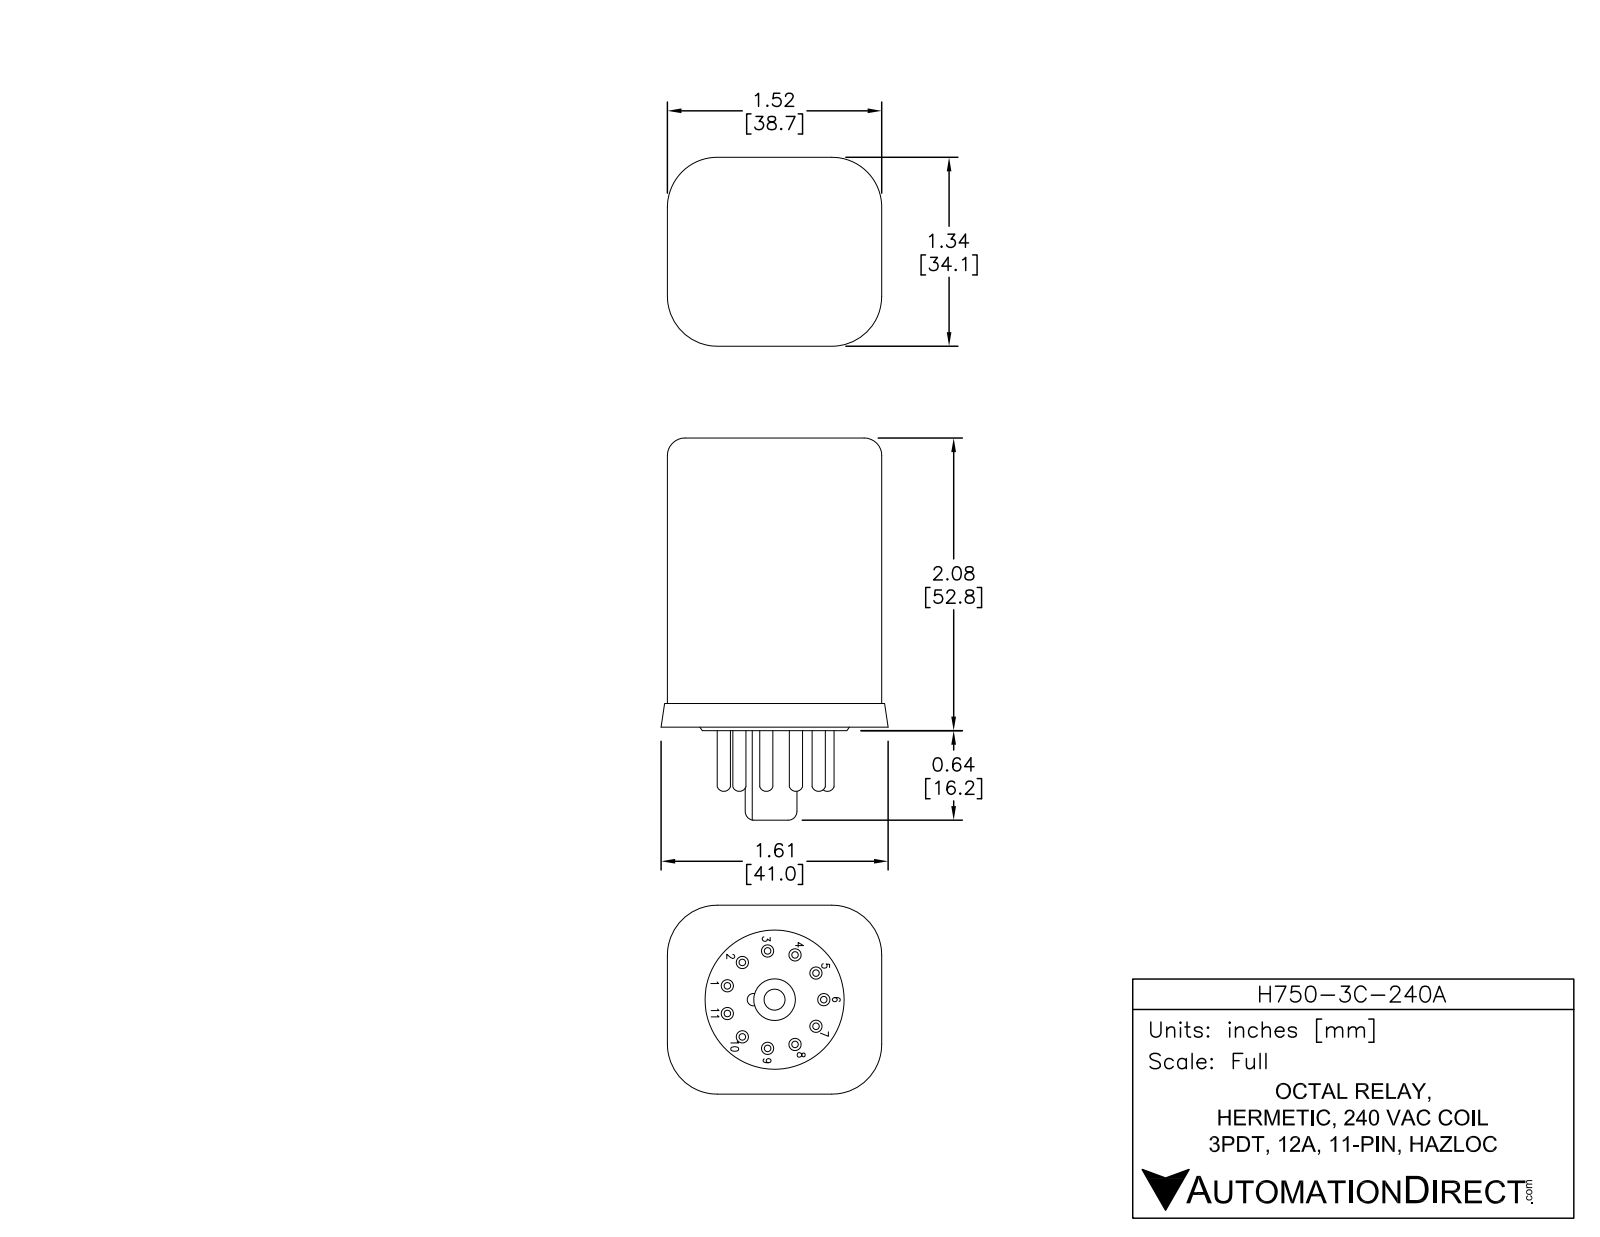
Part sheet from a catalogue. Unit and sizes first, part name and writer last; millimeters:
Units: millimetres
Overall size (bounding box): 67.3 × 41.35 × 36.6
Round holes (diameter × count): ⌀4.5 ×8, ⌀3.9 ×1
Round bosses / shafts (diameter × count): ⌀2.31 ×8, ⌀27 ×1, ⌀12 ×1, ⌀8 ×1
Partial cylindrical surfaces — rounded edges, fillets, slot ends (radius × count): R0.62 ×8, R2.5 ×4, R10 ×4, R11.3 ×4, R0.5 ×2, R0.59 ×1
Main face-to-face distances: 53, 34, 38.75, 0.5, 53.5, 1.3, 35.3, 40.05, 1, 54
Hole centre spacings: 8.5, 12.02, 15.7, 6.5, 6.51, 16.99
Volume: 66 961 mm³ · Surface area: 10 715 mm²
Bodies: 1 solid, 290 faces (124 planar, 65 cylindrical, 101 other)
Part name (STEP PRODUCT): H750-3C-240A
STEP written by: SolidWorks 2013 (AUTOMOTIVE_DESIGN)
